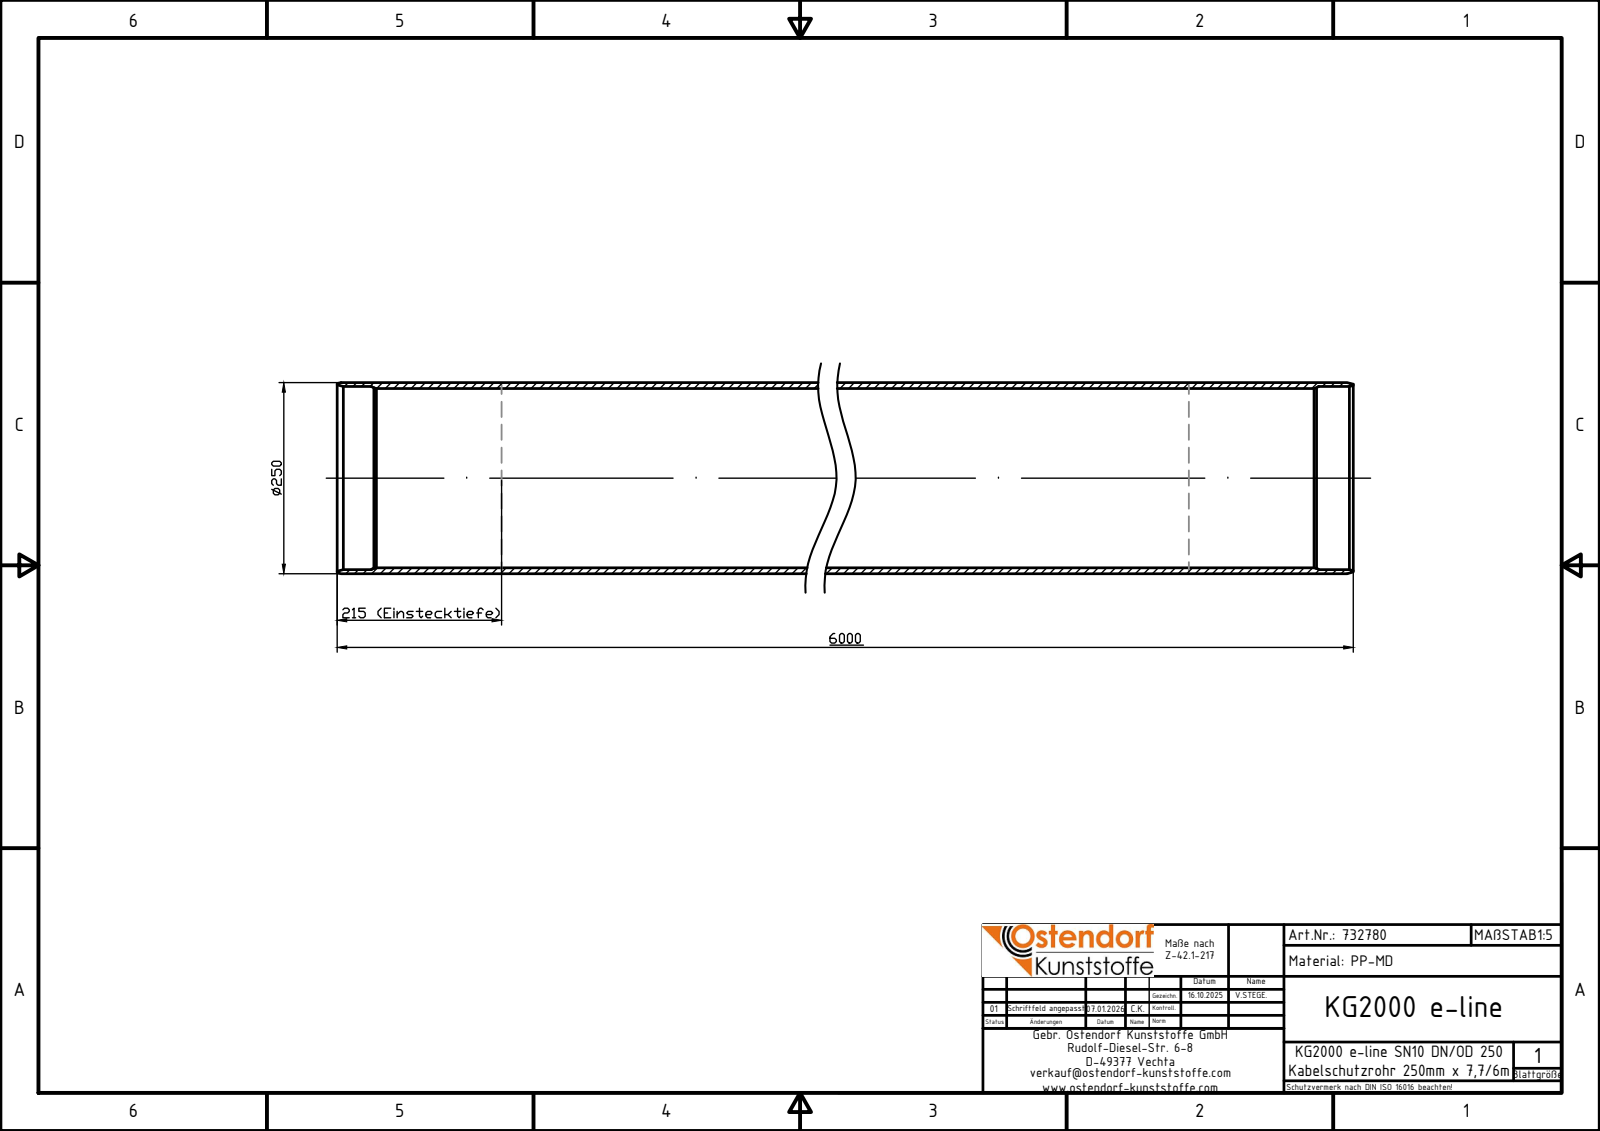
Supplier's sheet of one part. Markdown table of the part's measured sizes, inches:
| quantity | value |
| --- | --- |
| part name | 732780z |
| STEP written by | Autodesk Inventor 2024 (AUTOMOTIVE_DESIGN) |
| units | inches |
| bodies | 1 solid, 16 faces (2 planar, 4 cylindrical, 10 other) |
| overall size | 236.22 × 9.843 × 9.843 |
| volume | 2 134 in³ |
| surface area | 14 170 in² |
| round holes (diameter × count) | 9.236 × 1, 9.433 × 1 |
| round bosses / shafts (diameter × count) | 9.843 × 1 |
| main face-to-face distances | 236.22 |
